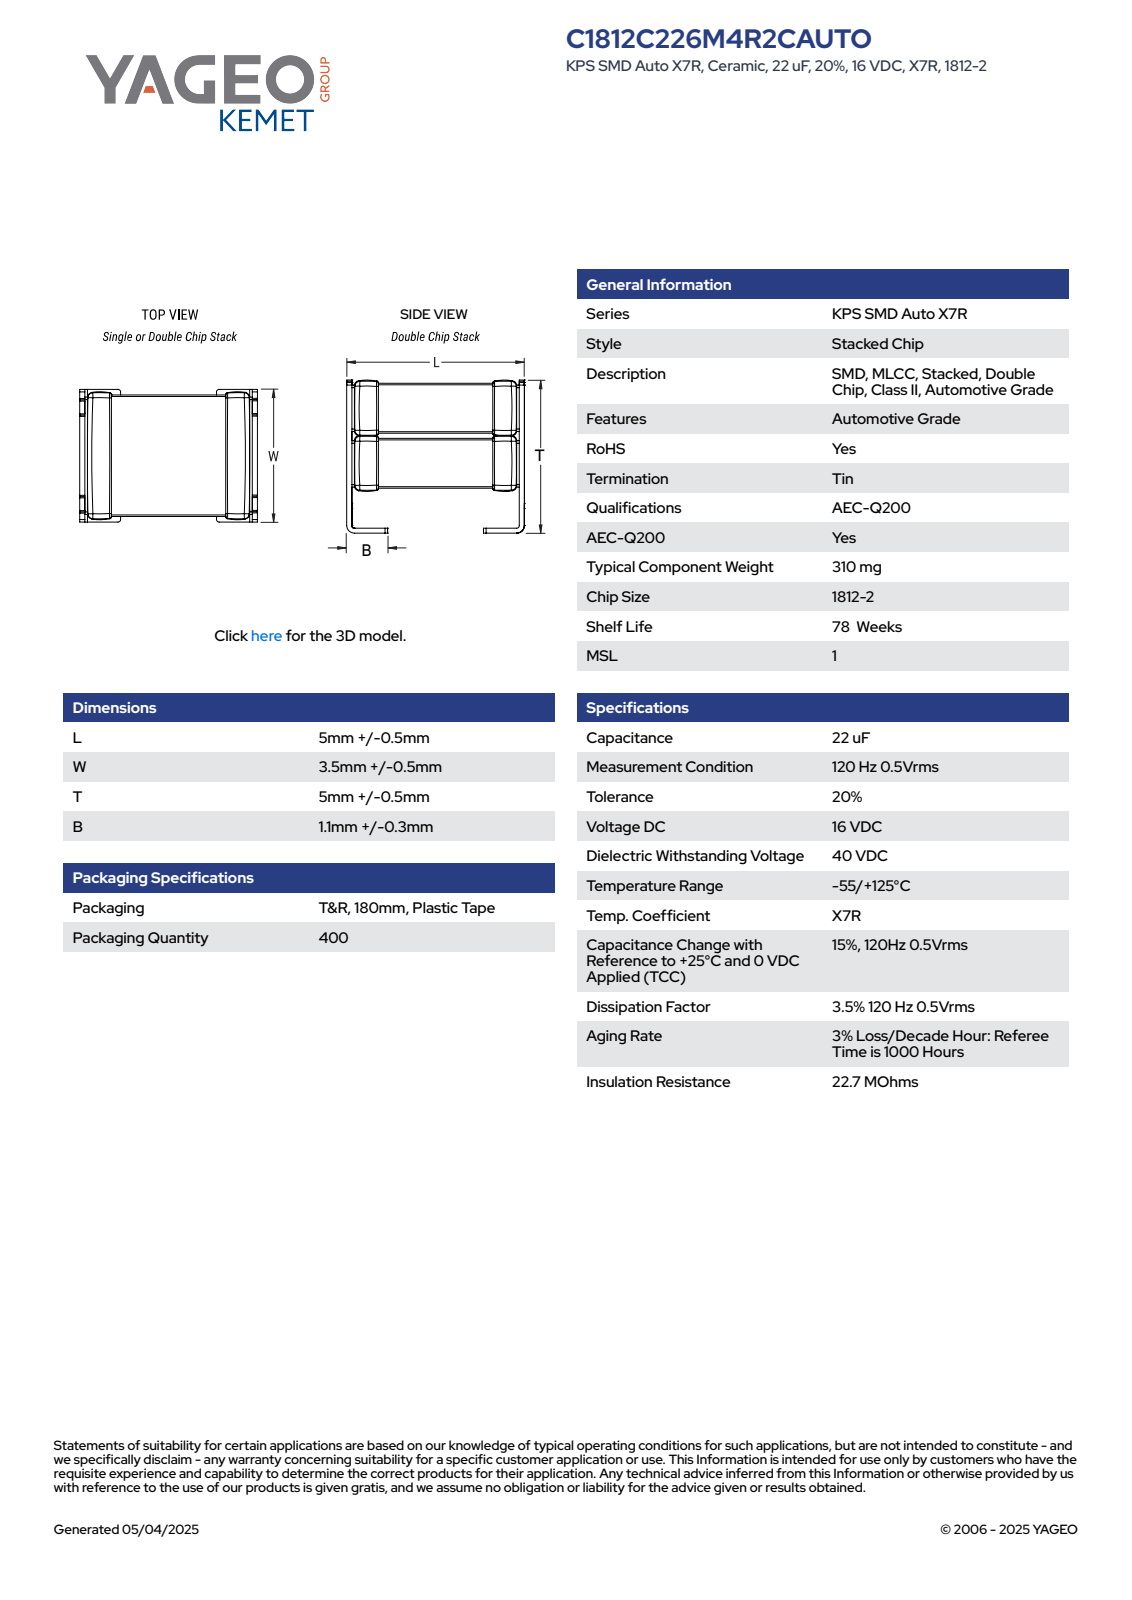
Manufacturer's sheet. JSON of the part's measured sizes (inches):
{"part_name": "CCSS_S2_1812-2_L5.5W4T5.5B1.4", "step_written_by": "SolidWorks 2014 (AUTOMOTIVE_DESIGN)", "units": "inches", "bodies": {"solids": 4, "faces": 113, "planar": 109, "cylindrical": 4, "other": 0}, "overall_size": [0.217, 0.217, 0.157], "volume_in3": 0.005, "surface_area_in2": 0.321, "face_to_face_distances": [0.217, 0.213, 0.068, 0.069, 0.065, 0.135, 0.067, 0.071, 0.066, 0.063]}
